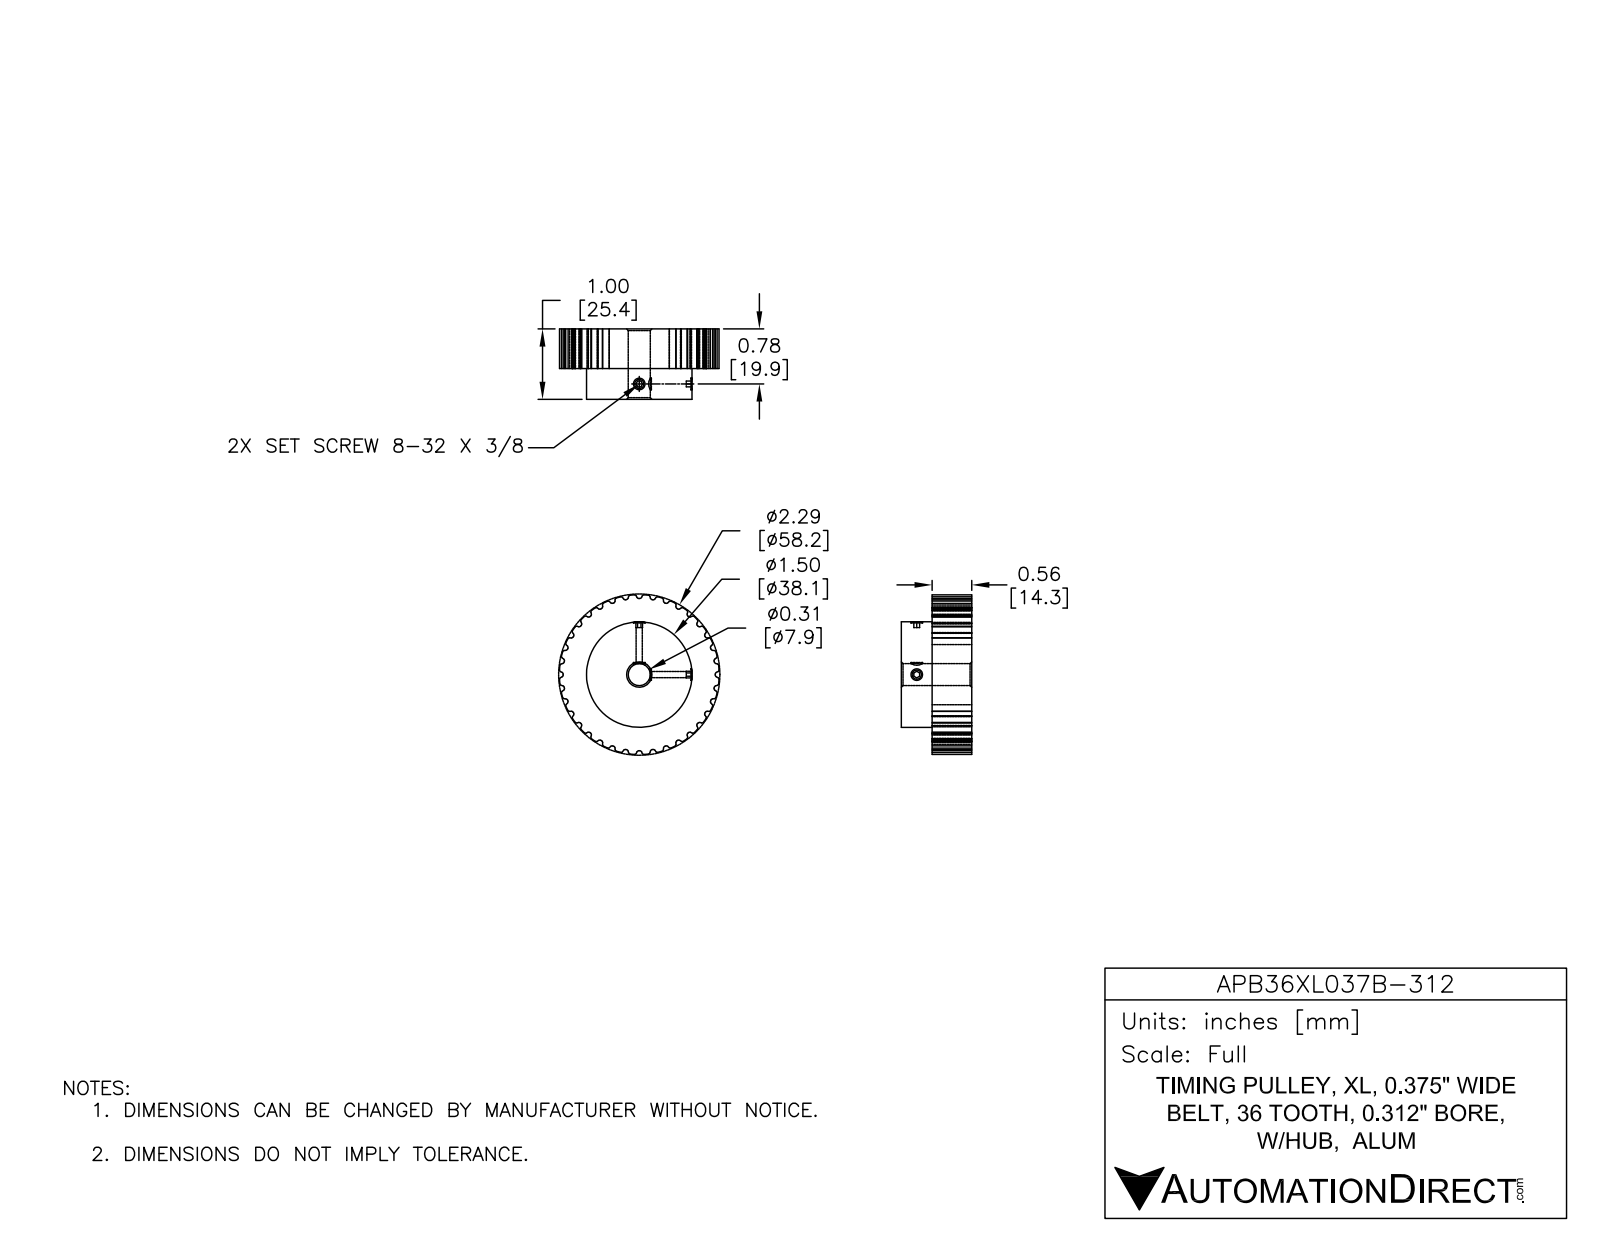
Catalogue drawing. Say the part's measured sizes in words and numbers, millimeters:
The part is named "APB36XL037BF-312". Its 3-D file was written by "SolidWorks 2014 (AUTOMOTIVE_DESIGN)". It is 1 solid with 334 faces: 75 planar, 249 cylindrical and 10 other. Overall it measures 57.7 by 57.7 by 25.4 millimeters. Its volume is 47 160 cubic millimeters and its surface area 10 420 square millimeters. Round holes: 2 of diameter 2.2, 1 of diameter 8. Round bosses or shafts: 1 of diameter 38.1. Partial cylindrical surfaces (rounded edges, fillets, slot ends): 144 of radius 0.4, 1 of radius 27.5, 1 of radius 28.9. The main face-to-face distances are 14.2, 25.4, 11.2, 22, 22, 22, 22.1.
